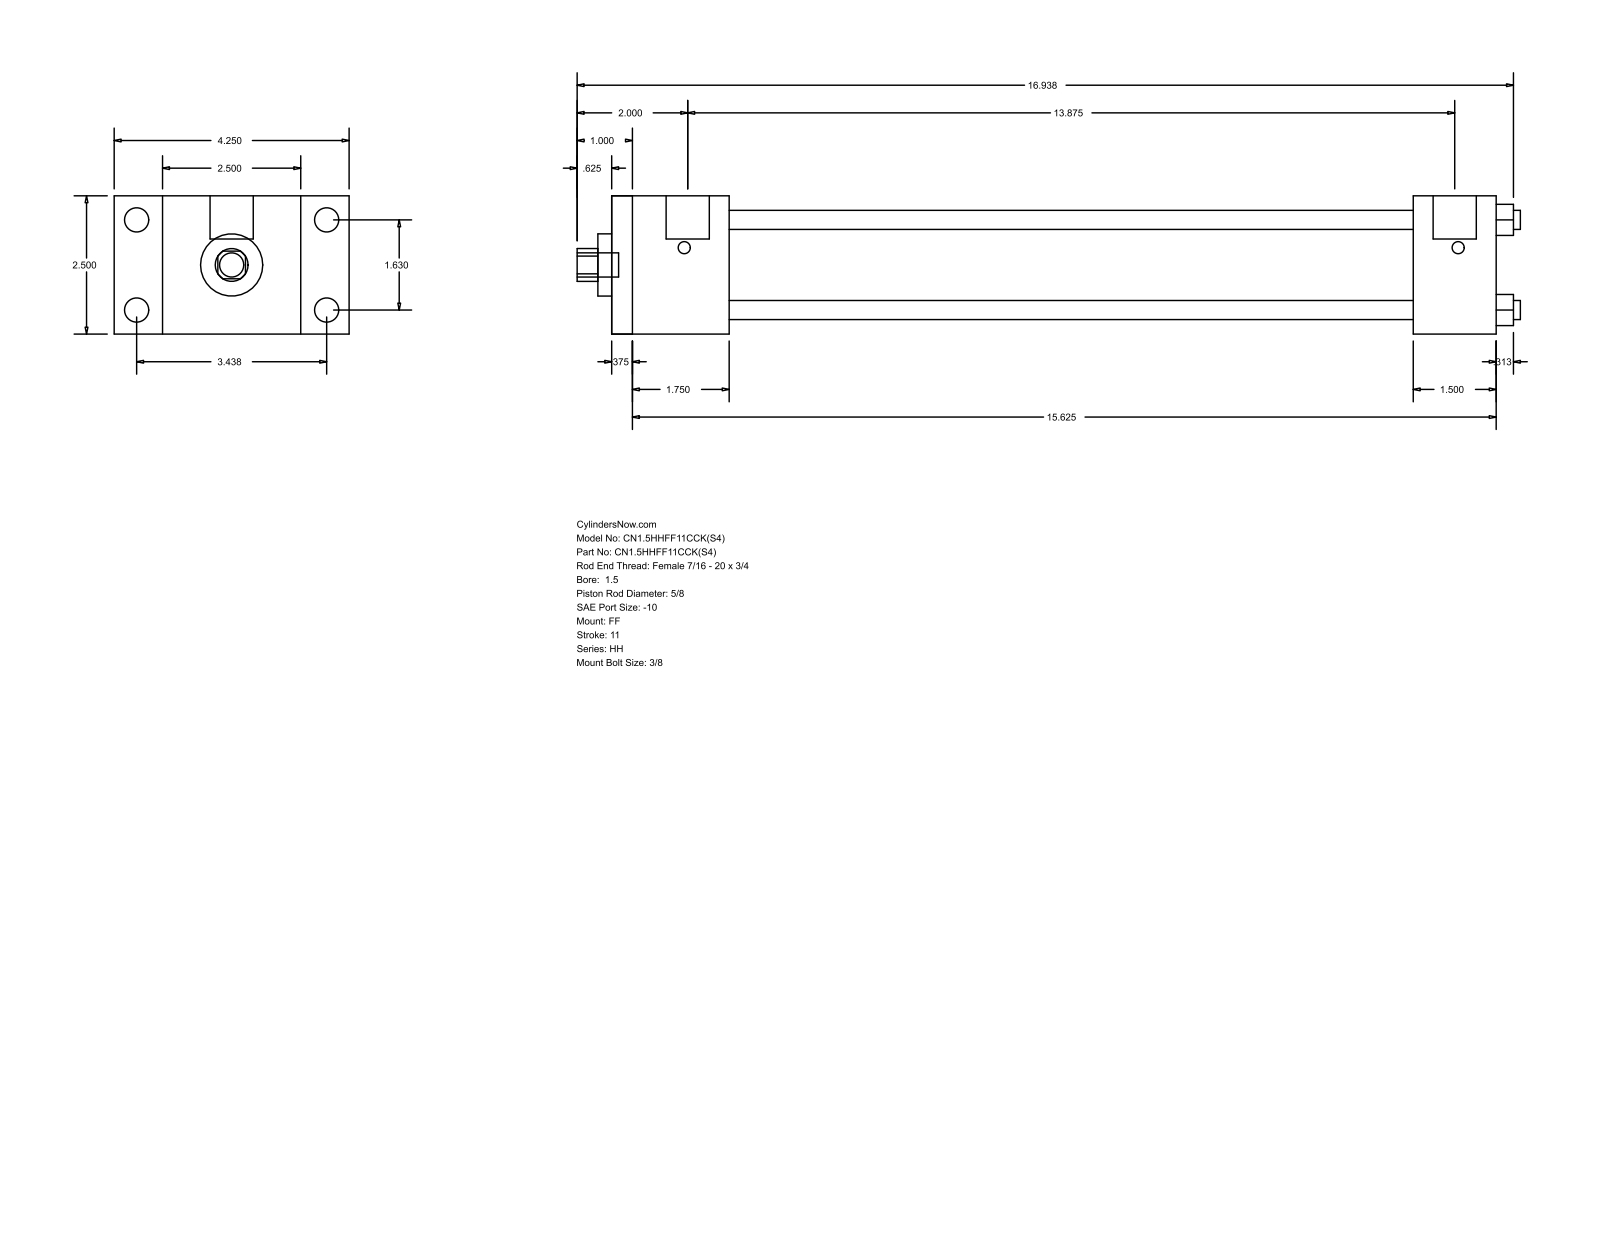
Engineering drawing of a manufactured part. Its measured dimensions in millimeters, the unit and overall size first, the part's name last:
Units: millimetres
Overall size (bounding box): 433.39 × 107.95 × 63.5
Round holes (diameter × count): ⌀8.76 ×4, ⌀15.88 ×1, ⌀28.57 ×1, ⌀44.45 ×1
Round bosses / shafts (diameter × count): ⌀11.13 ×4, ⌀5.56 ×4, ⌀19.84 ×2, ⌀11.11 ×1
Partial cylindrical surfaces — rounded edges, fillets, slot ends (radius × count): R7.54 ×1
Main face-to-face distances: 63.5, 406.39, 9.52, 396.87, 53.97, 44.45, 352.42, 368.3, 358.78, 314.33
Hole centre spacings: 29.27, 41.4, 58.55
Bodies: 0 solids, 92 faces (64 planar, 28 cylindrical, 0 other)
Part name (STEP PRODUCT): HH_FF__0150_0.625
STEP written by: GSSL Pune (CONFIG_CONTROL_DESIGN)
